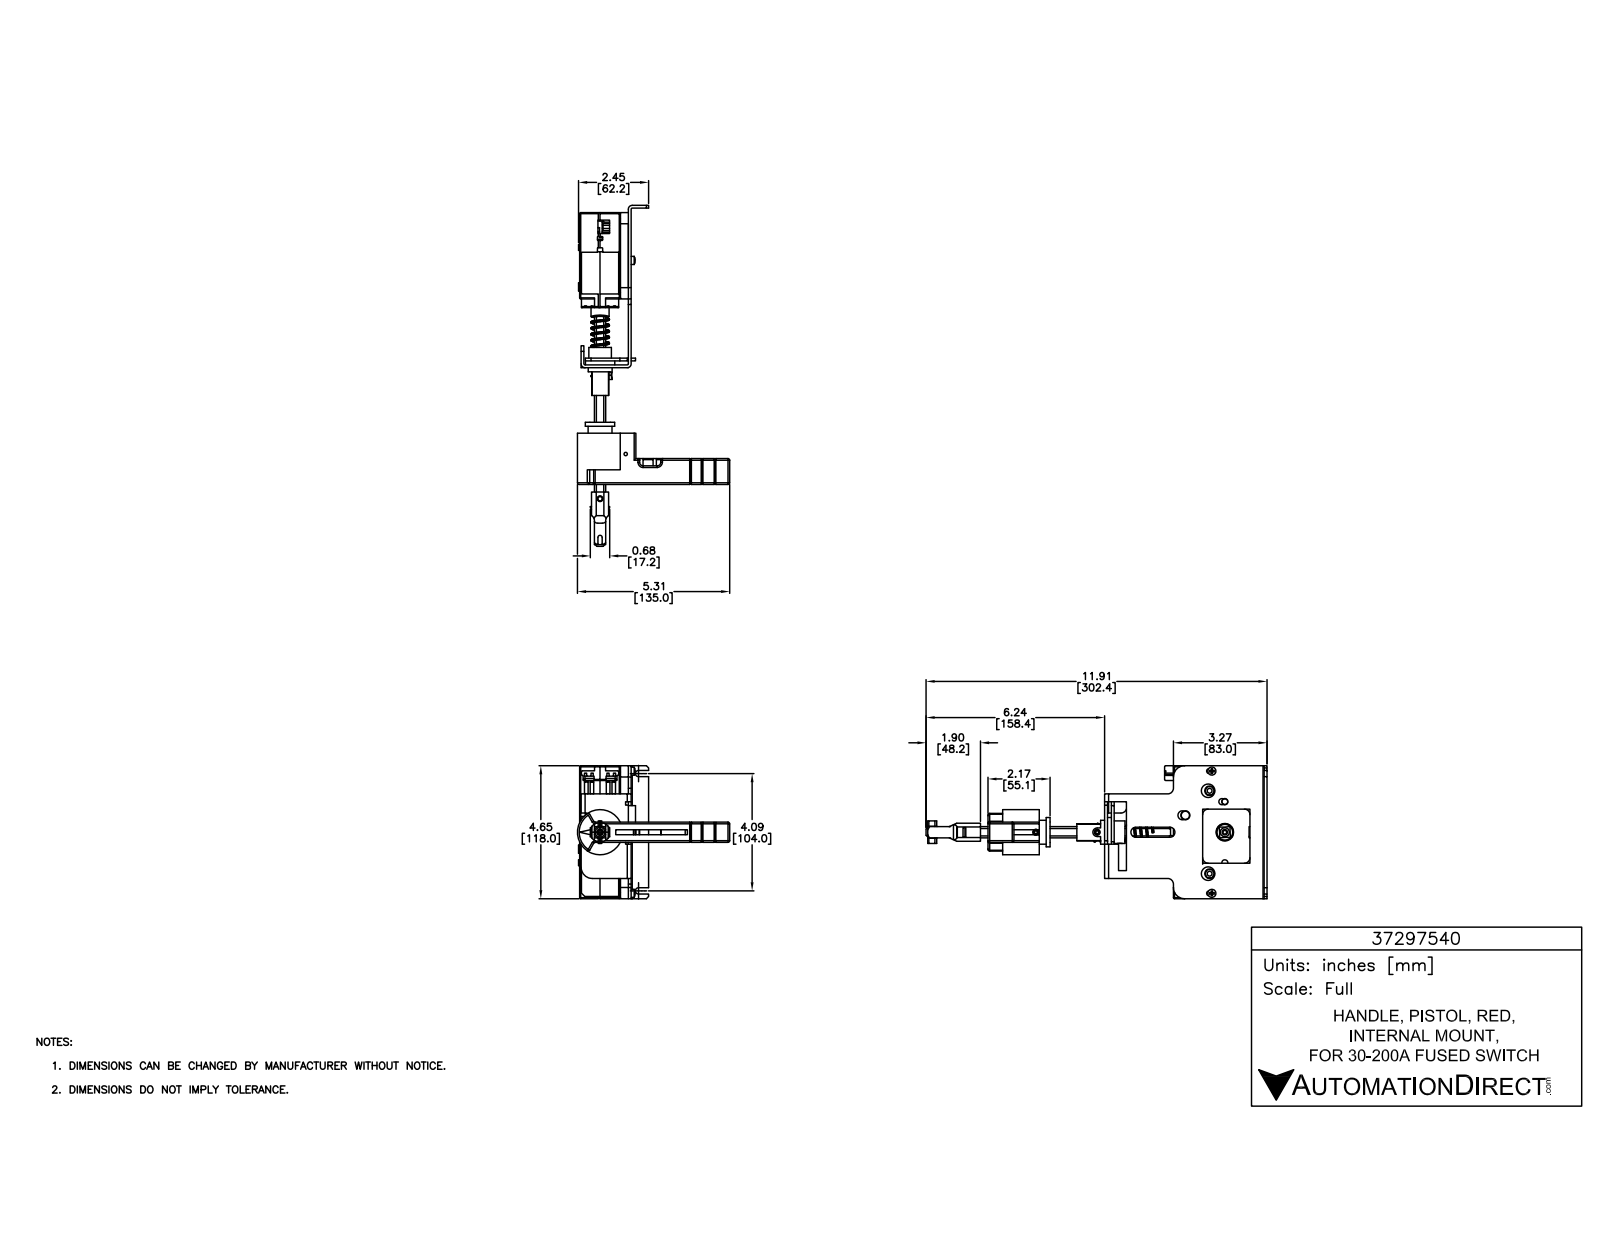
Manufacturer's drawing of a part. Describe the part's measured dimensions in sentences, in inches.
The part is named "37297540". Its 3-D file was written by "SolidWorks 2015 (AUTOMOTIVE_DESIGN)". It is 17 solids with 2093 faces: 505 planar, 477 cylindrical and 1111 other. Overall it measures 11.906 by 5.315 by 4.646 inches. Its volume is 10.21 cubic inches and its surface area 183 square inches. Round holes: 3 of diameter 0.165, 2 of diameter 0.173, 2 of diameter 0.335, 2 of diameter 0.472, 1 of diameter 0.118, 1 of diameter 0.157, 1 of diameter 0.161, 1 of diameter 0.205, 1 of diameter 0.217, 1 of diameter 0.315, 1 of diameter 0.323, 1 of diameter 0.374. Round bosses or shafts: 3 of diameter 0.197, 2 of diameter 1.024, 2 of diameter 0.833, 2 of diameter 0.283, 2 of diameter 0.157, 1 of diameter 1.575, 1 of diameter 0.787. Partial cylindrical surfaces (rounded edges, fillets, slot ends): 104 of radius 0.059, 96 of radius 0.02, 28 of radius 0.197, 15 of radius 0.039, 7 of radius 0.118, 6 of radius 0.083, 5 of radius 0.394, 4 of radius 0.01. The main face-to-face distances are 0.098, 0.276, 0.374, 0.157, 0.236, 0.551, 5.571, 0.268, 5.335, 0.441. The hole center spacings are 0.051, 0.689, 0.691, 0.699, 2.894, 2.894, 3.581, 3.583.
